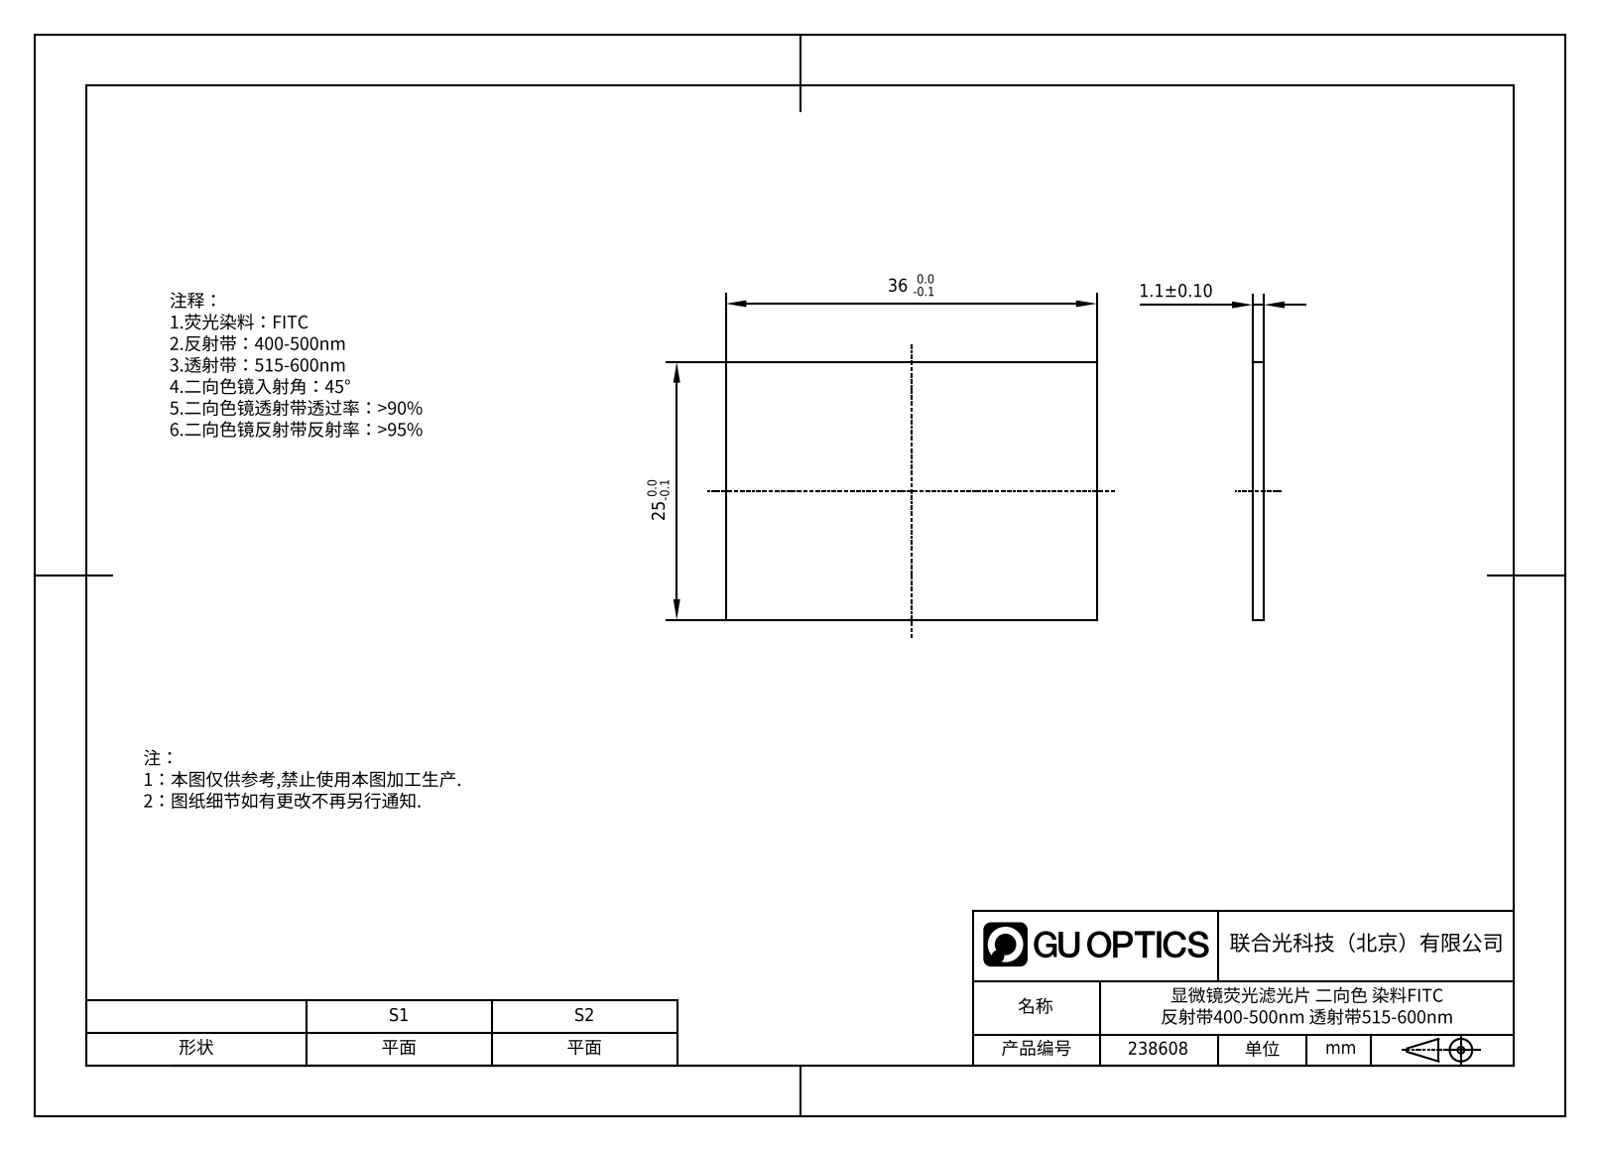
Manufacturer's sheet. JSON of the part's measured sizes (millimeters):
{"part_name": "GDMLPH-510-25x36S", "step_written_by": "SolidWorks 2022 (AUTOMOTIVE_DESIGN)", "units": "millimeters", "bodies": {"solids": 1, "faces": 6, "planar": 6, "cylindrical": 0, "other": 0}, "overall_size": [36, 25, 1.1], "volume_mm3": 990, "surface_area_mm2": 1934, "face_to_face_distances": [1.1, 25, 36]}
